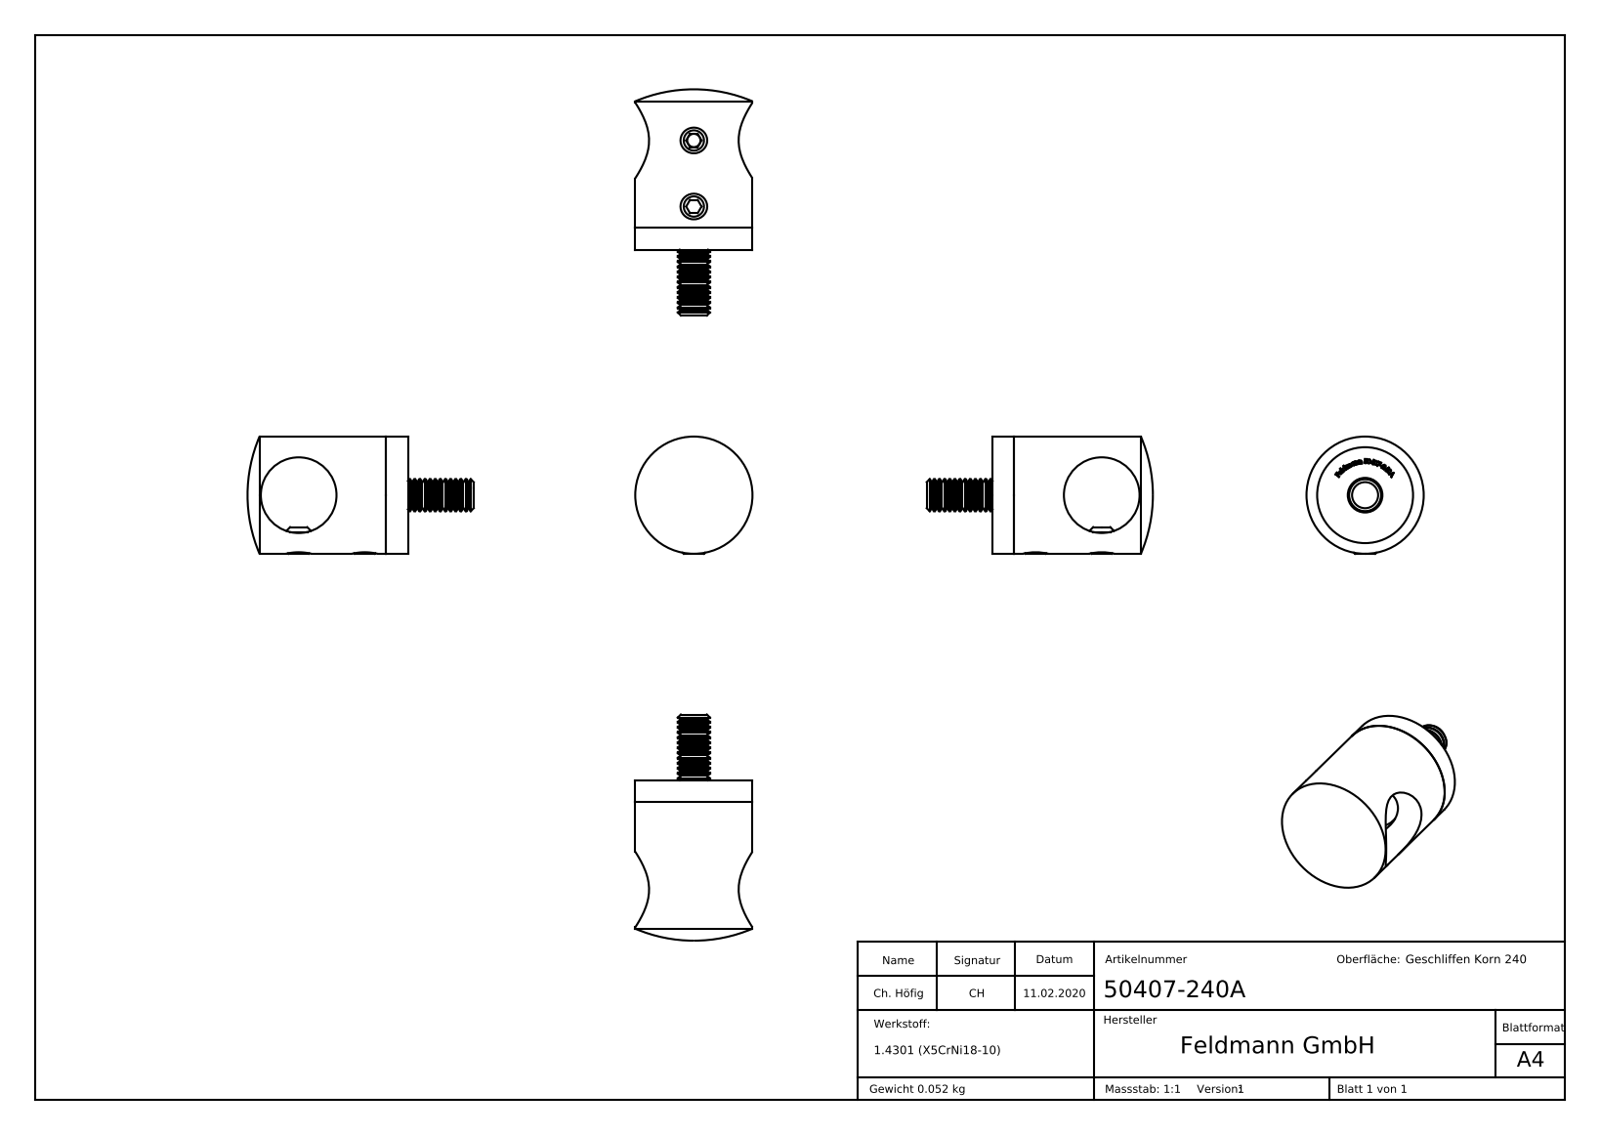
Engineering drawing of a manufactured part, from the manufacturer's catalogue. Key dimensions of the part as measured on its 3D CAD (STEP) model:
Part name (STEP PRODUCT): socket countersunk head screw_din; DIN914; Querstabhalter Teil1 Konfig_50XXX-240A Teil1 14,2; 50407-240A (+7 more)
STEP written by: SolidWorks 2015 (CONFIG_CONTROL_DESIGN)
Units: millimetres
Bodies: 5 solids, 364 faces (182 planar, 35 cylindrical, 147 other)
Overall size (bounding box): 70 × 42.45 × 22
Volume: 7 287 mm³ · Surface area: 5 883 mm²
Round holes (diameter × count): ⌀4.2 ×2, ⌀6.5 ×1, ⌀12 ×1, ⌀14.2 ×1, ⌀18 ×1
Round bosses / shafts (diameter × count): ⌀5 ×2, ⌀22 ×1, ⌀11.9 ×1, ⌀11.57 ×1, ⌀6 ×1
Main face-to-face distances: 2.1, 2, 4.1, 12.65, 10.65, 8.55, 2.5, 11.6, 9.6, 7.5
Hole centre spacings: 12.4
